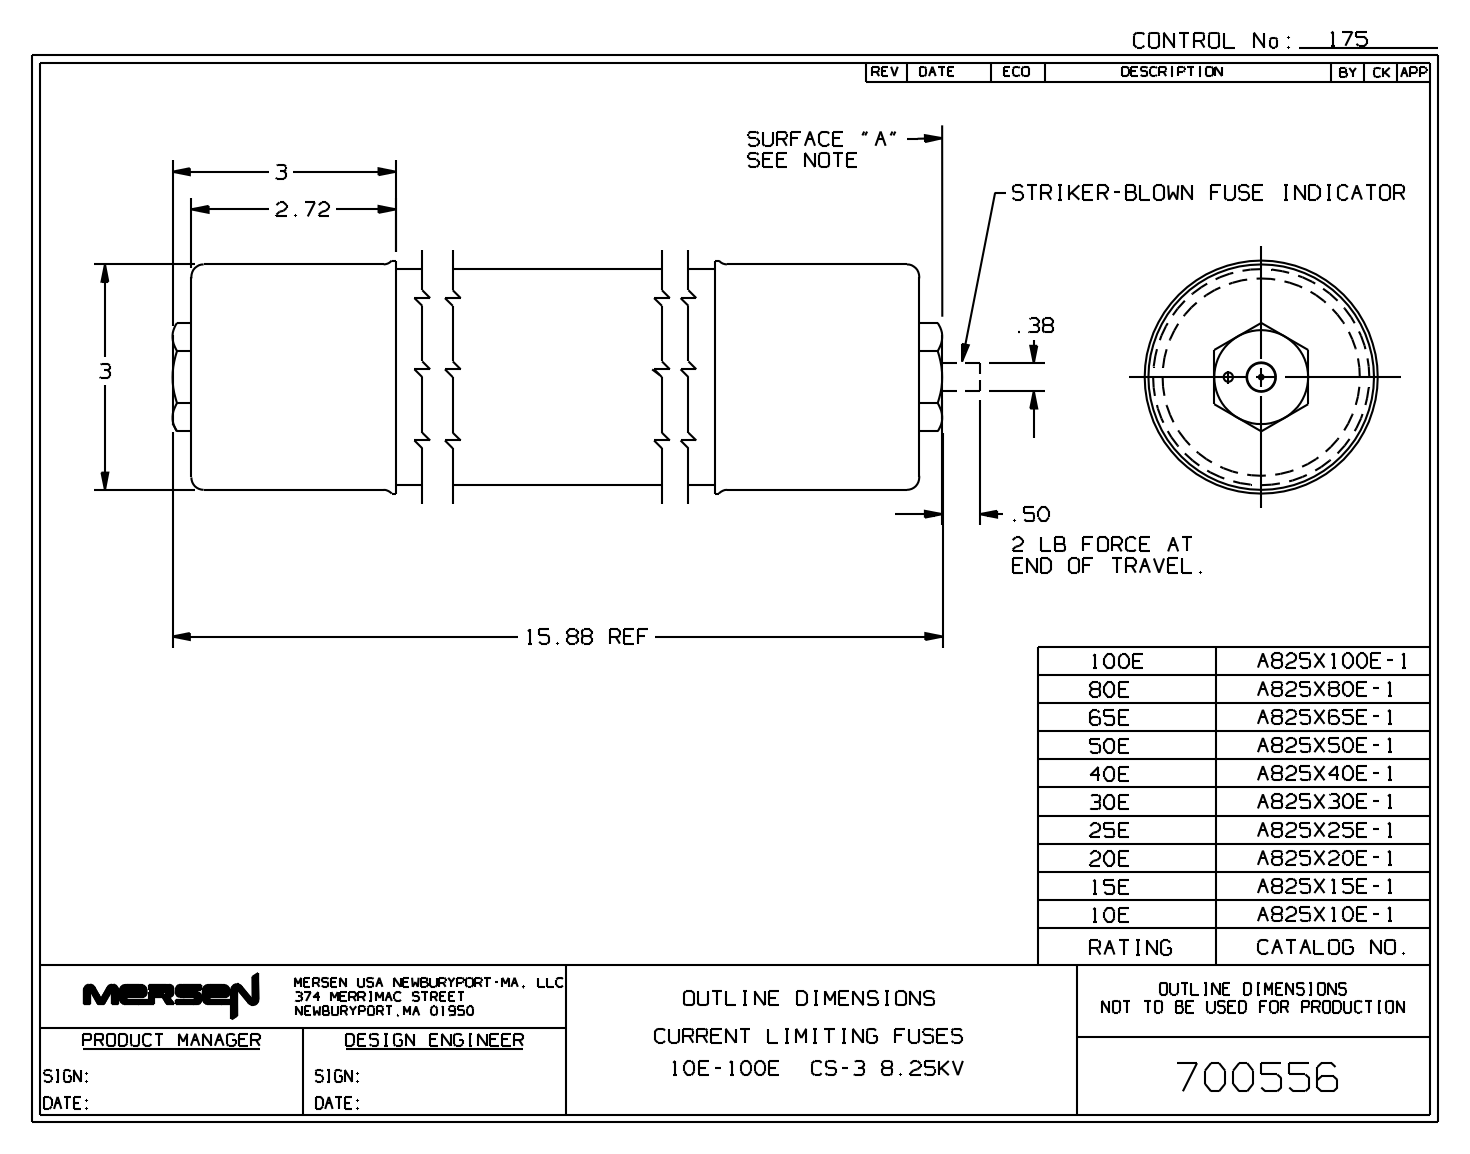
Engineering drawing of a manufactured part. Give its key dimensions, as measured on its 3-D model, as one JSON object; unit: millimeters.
{"part_name": "700556", "step_written_by": "SolidWorks 2013 (AUTOMOTIVE_DESIGN)", "units": "millimeters", "bodies": {"solids": 10, "faces": 340, "planar": 79, "cylindrical": 176, "other": 85}, "overall_size": [403.4, 78.7, 78.7], "volume_mm3": 436700, "surface_area_mm2": 288500, "round_holes": [[3.2, 13], [3.2, 6], [6.4, 6], [0.5, 1], [1.6, 1], [3.7, 1], [4.8, 1], [9.9, 1], [11.8, 1], [13, 1], [20.7, 1], [23, 1]], "round_bosses_or_shafts": [[76.1, 1], [73, 1], [66.5, 1], [63.5, 1], [60.2, 1], [31.8, 1], [30.2, 1], [25.4, 1]], "face_to_face_distances": [384.6, 368.7, 15.9, 15.9, 352.8, 368.7, 1.4, 385.7, 1.4, 17.3], "hole_center_spacings": [368.8, 17.4, 20.3, 24.7, 42.6, 8.4, 11.1, 16.6]}
